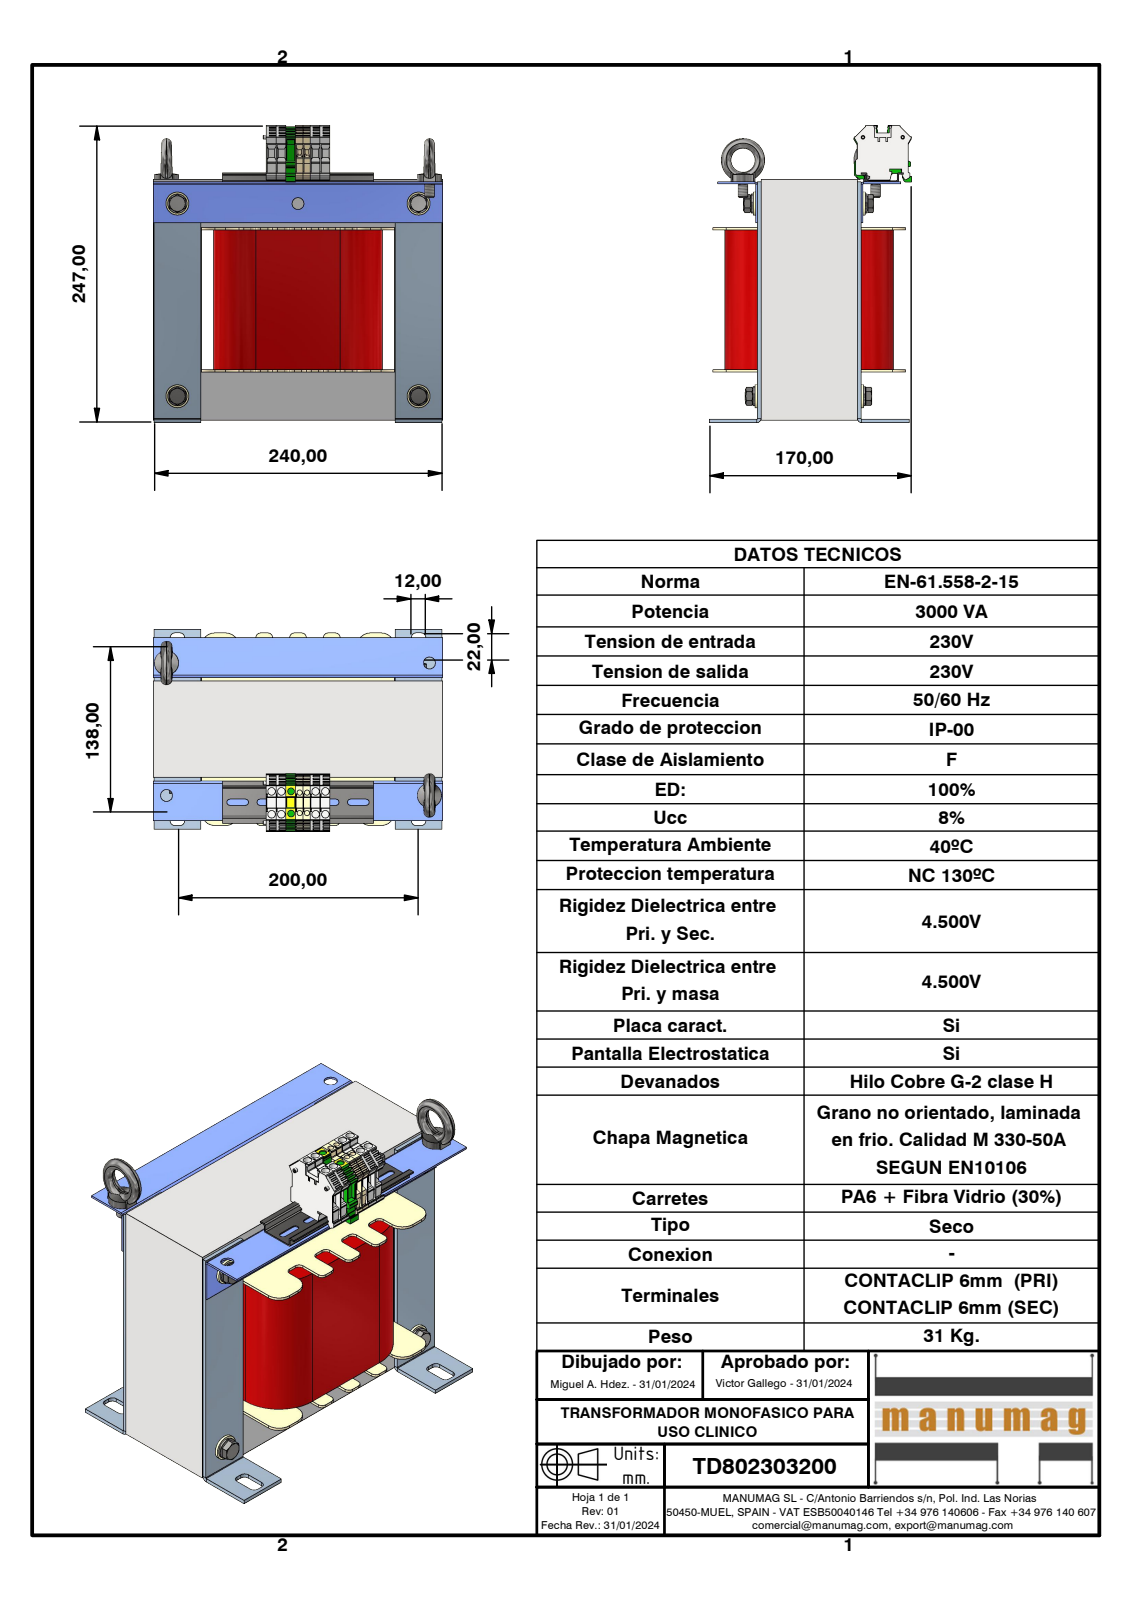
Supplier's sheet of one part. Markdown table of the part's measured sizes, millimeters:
| quantity | value |
| --- | --- |
| part name | TD802303200; EI240 240 x 200 - 80 (Rc80); SEMI 40 X 60 RC80 EI240 - 40; Escuadra RC80 (+8 more) |
| STEP written by | Autodesk Inventor 2023 (AUTOMOTIVE_DESIGN) |
| units | millimeters |
| bodies | 42 solids, 2415 faces (1680 planar, 567 cylindrical, 168 other) |
| overall size | 247.05 × 240 × 168.1 |
| volume | 4 799 000 mm³ |
| surface area | 583 000 mm² |
| round holes (diameter × count) | 6.3 × 8, 10 × 7, 2.4 × 4, 2.5 × 4, 2.75 × 4, 4.3 × 4, 6.65 × 4, 8 × 4, 8.4 × 4, 11 × 4, 12 × 4, 2.95 × 2 |
| round bosses / shafts (diameter × count) | 19 × 4, 16 × 4, 11.4 × 4, 9.6 × 4, 7.32 × 4, 36 × 2, 8 × 2, 7 × 2 |
| partial cylindrical surfaces (radius × count) | 4 × 48, 0.3 × 30, 1 × 22, 0.25 × 17, 0.5 × 13, 2.6 × 10, 2 × 9, 0.4 × 8 |
| main face-to-face distances | 80, 160, 40, 3, 200, 83, 120, 2, 1.5, 30 |
| hole center spacings | 8.1, 15.23, 19, 20.65, 21.32, 23.56, 27.89, 36.5 |
